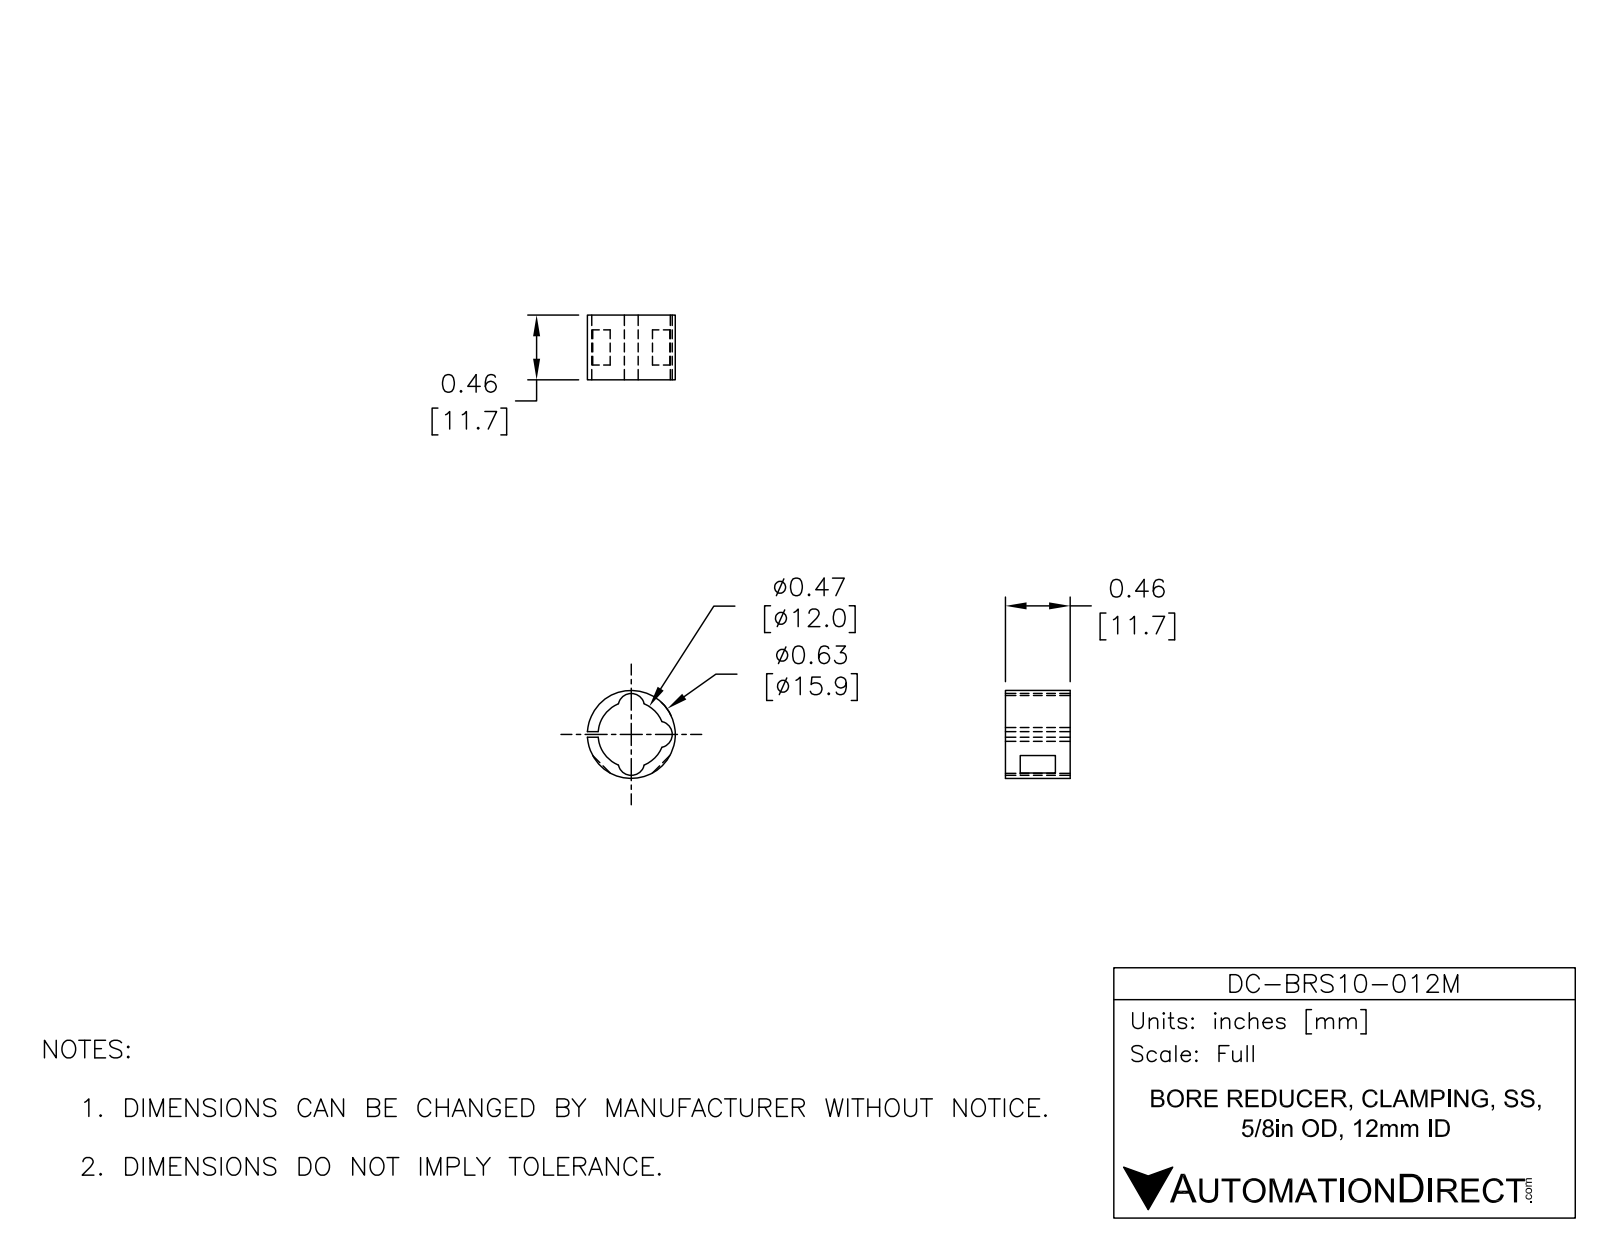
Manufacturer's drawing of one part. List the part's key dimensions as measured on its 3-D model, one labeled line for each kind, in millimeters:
Part name (STEP PRODUCT): DC-BRS10-12M
STEP written by: SolidWorks 2015 (AUTOMOTIVE_DESIGN)
Units: millimetres
Bodies: 1 solid, 21 faces (10 planar, 11 cylindrical, 0 other)
Overall size (bounding box): 15.88 × 15.86 × 11.68
Volume: 783 mm³ · Surface area: 1 242 mm²
Round bosses / shafts (diameter × count): ⌀15.88 ×1
Partial cylindrical surfaces — rounded edges, fillets, slot ends (radius × count): R2.38 ×3, R6 ×1
Main face-to-face distances: 11.68, 1.02, 2.67, 9.01, 6.34
